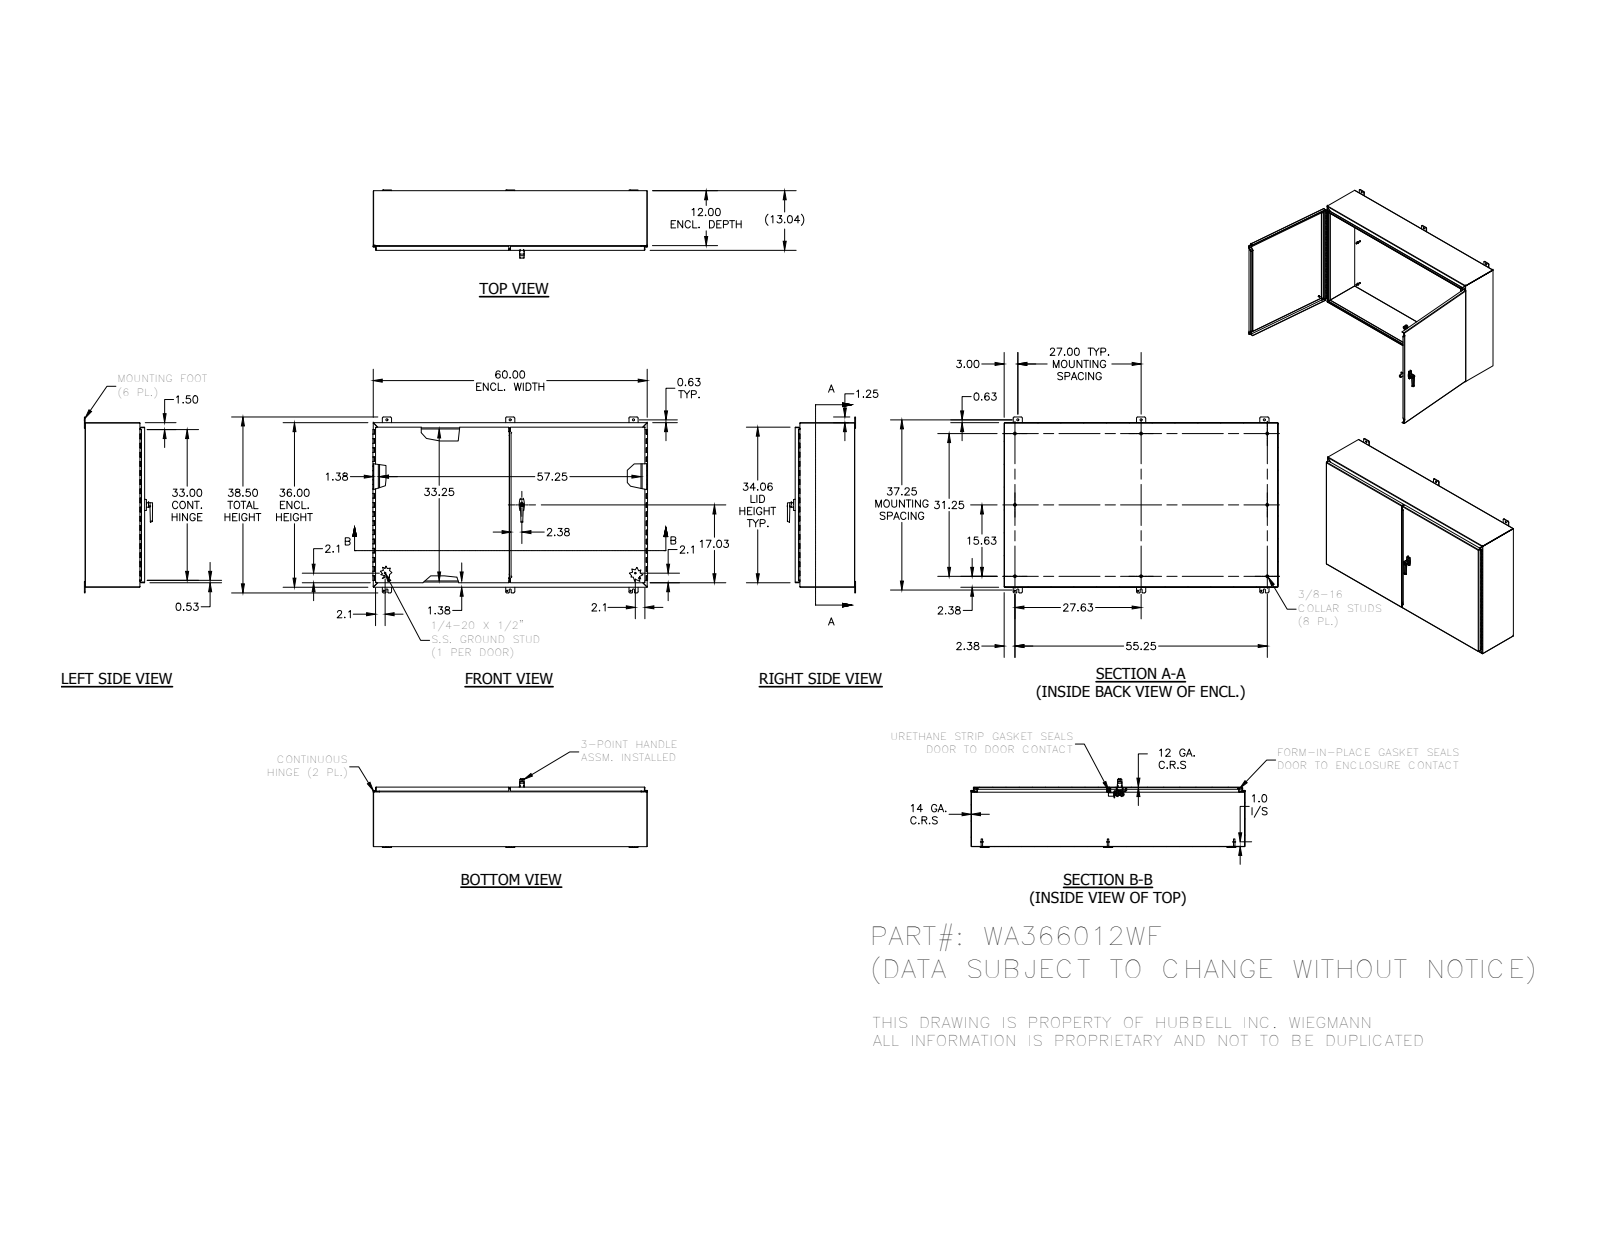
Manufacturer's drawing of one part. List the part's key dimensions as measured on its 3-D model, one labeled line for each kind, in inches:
Part name (STEP PRODUCT): WA366012WF; WA366012WFLRS; 34840; WA366012WFBTB (+8 more)
STEP written by: Autodesk Inventor 2012 (AUTOMOTIVE_DESIGN)
Units: inches
Bodies: 62 solids, 2660 faces (1474 planar, 694 cylindrical, 492 other)
Overall size (bounding box): 60.148 × 38.5 × 14.919
Volume: 648.4 in³ · Surface area: 15 358 in²
Round holes (diameter × count): ⌀0.277 ×8, ⌀0.083 ×6, ⌀0.313 ×6, ⌀0.438 ×6, ⌀0.2 ×4, ⌀0.125 ×2, ⌀0.159 ×2, ⌀0.241 ×2, ⌀0.25 ×2, ⌀0.252 ×2, ⌀0.4 ×2, ⌀0.407 ×2
Round bosses / shafts (diameter × count): ⌀0.625 ×8, ⌀0.33 ×8, ⌀0.157 ×7, ⌀0.25 ×4, ⌀0.115 ×4, ⌀1 ×2, ⌀0.563 ×2, ⌀0.527 ×2
Partial cylindrical surfaces — rounded edges, fillets, slot ends (radius × count): R0.031 ×28, R0.25 ×24, R0.008 ×22, R0.016 ×22, R0.105 ×17, R0.01 ×16, R0.05 ×14, R0.125 ×12
Main face-to-face distances: 0.074, 0.094, 12.942, 12.868, 13.035, 12.961, 35.926, 59.926, 35.852, 36
Hole centre spacings: 27, 45, 0.293, 0.201, 1.593, 26.352, 27.724, 36
